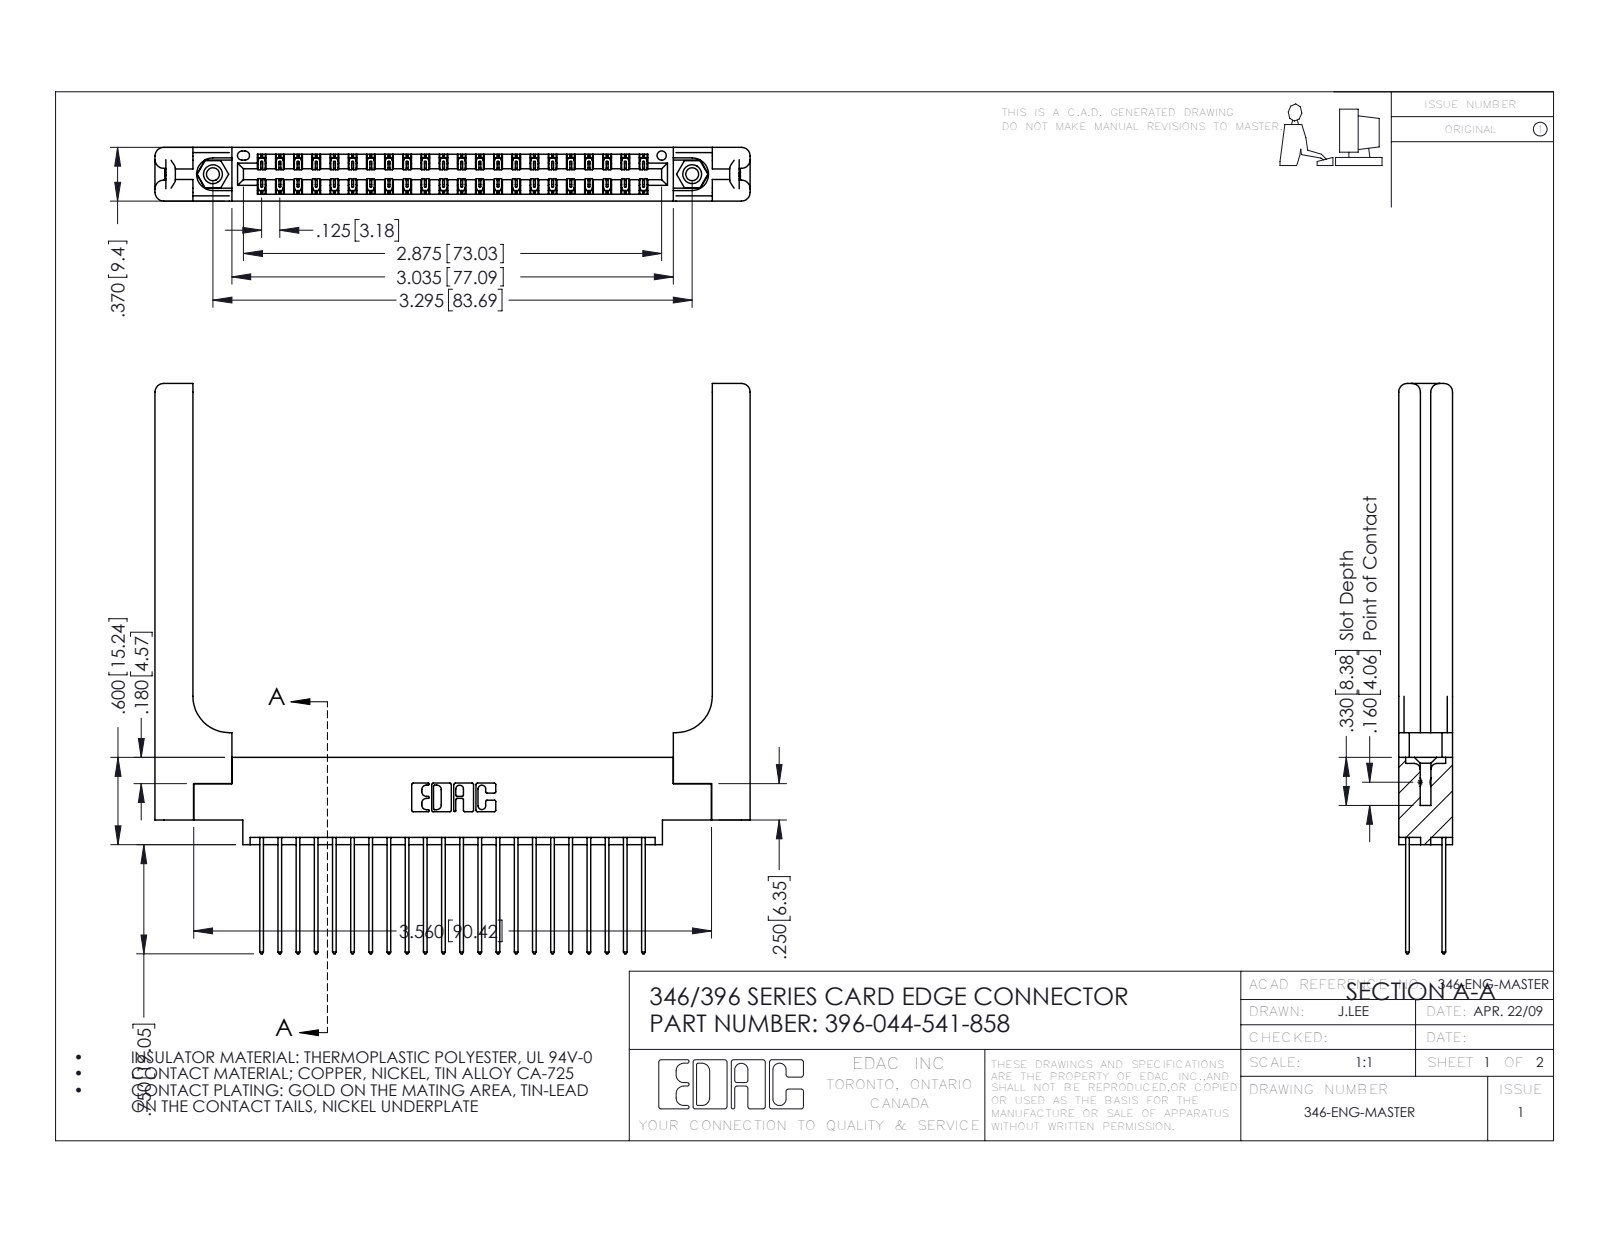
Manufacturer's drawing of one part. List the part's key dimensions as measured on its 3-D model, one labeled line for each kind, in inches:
Part name (STEP PRODUCT): 345-250-001_345-250-001-102; 345-292-001_345-293-141; 346 Part_0.170 Offset - 0.156 Dia-TH; 346-220-058_345-220-058 (+1 more)
STEP written by: SolidWorks 2016 (CONFIG_CONTROL_DESIGN)
Units: inches
Bodies: 49 solids, 2670 faces (1768 planar, 842 cylindrical, 60 other)
Overall size (bounding box): 4.091 × 3.92 × 0.37
Volume: 1.072 in³ · Surface area: 30.84 in²
Round holes (diameter × count): ⌀0.089 ×2, ⌀0.125 ×2, ⌀0.156 ×2, ⌀0.064 ×1
Round bosses / shafts (diameter × count): ⌀0.155 ×2
Partial cylindrical surfaces — rounded edges, fillets, slot ends (radius × count): R0.006 ×66, R0.01 ×44, R0.01 ×22, R0.06 ×16, R0.007 ×6, R0.031 ×6, R0.026 ×3, R0.014 ×2
Main face-to-face distances: 0.37, 0.072, 0.048, 0.322, 0.25, 0.148, 0.15, 0.025, 0.298, 0.275
Hole centre spacings: 0.246, 3.087, 3.295
